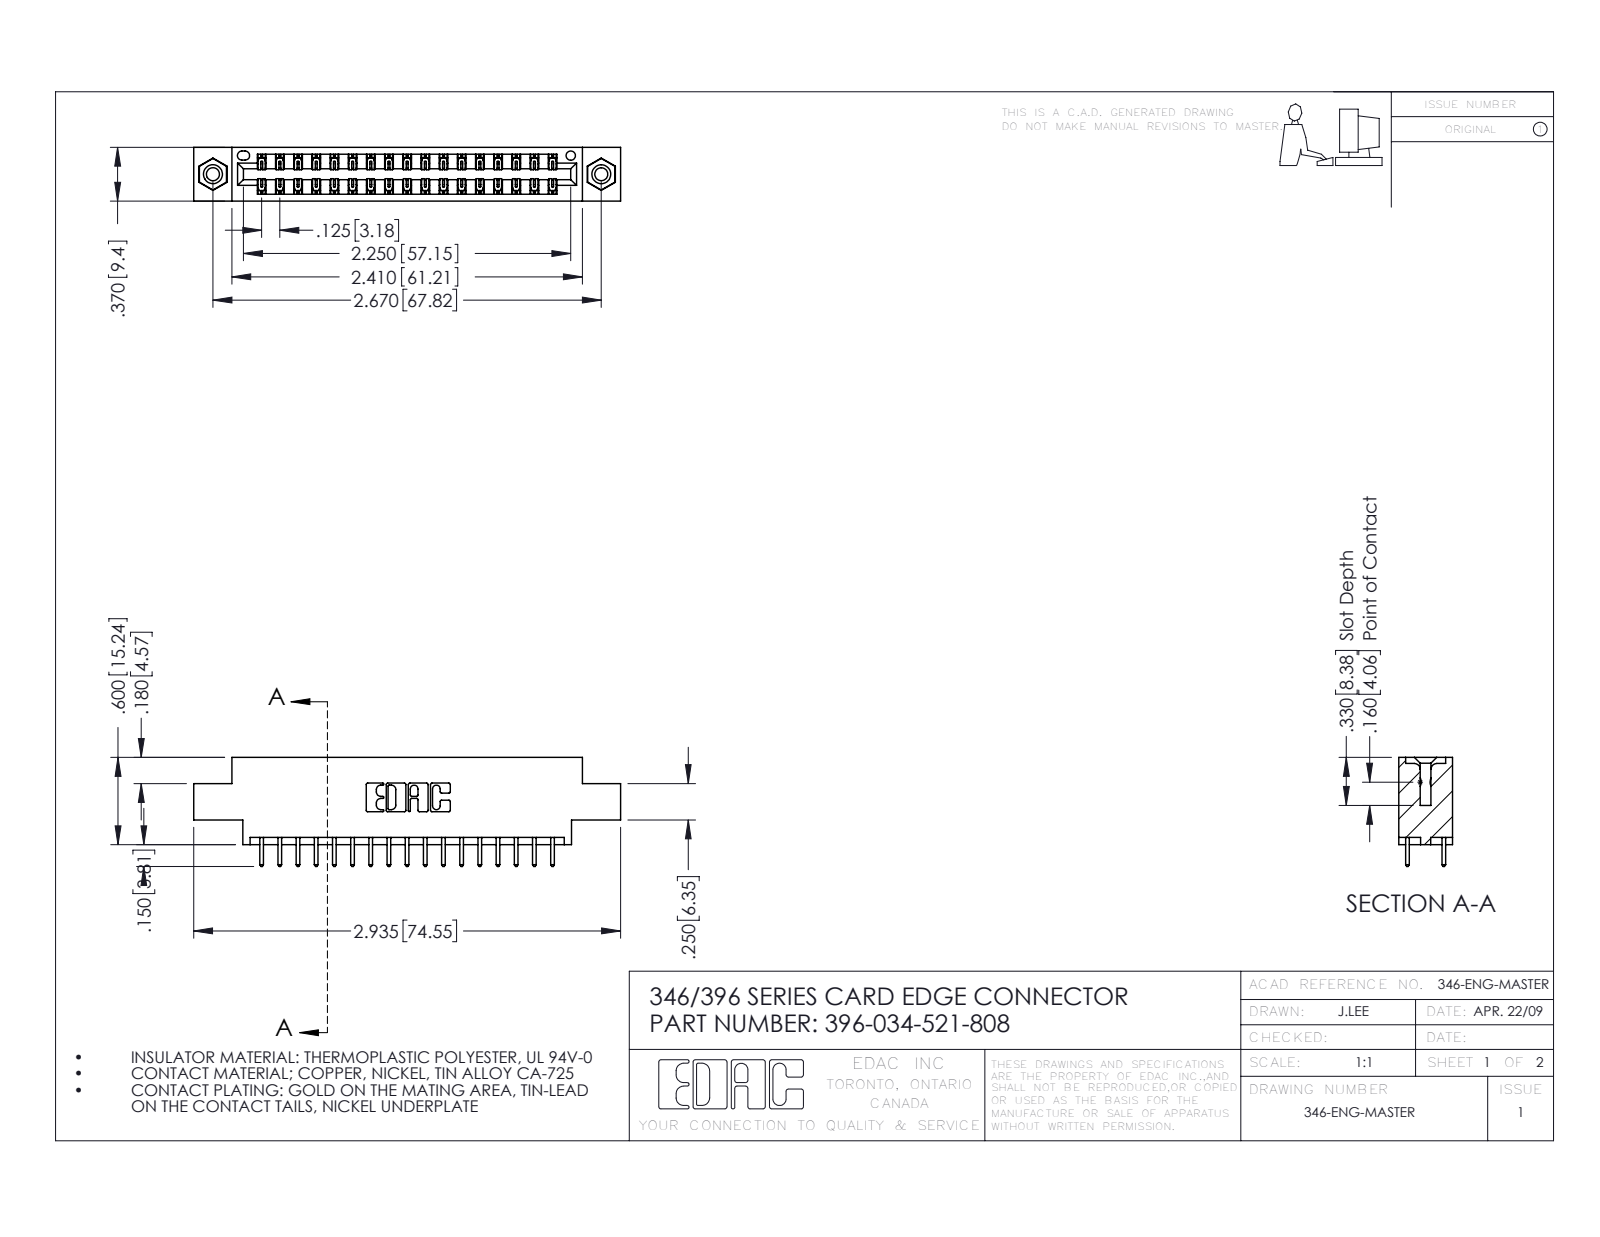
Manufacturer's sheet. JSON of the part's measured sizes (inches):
{"part_name": "345-292-001_345-293-121; 345-250-001_345-250-003-102; 396-034-521-808; 346 Part_0.170 Offset - 0.156 Dia-TI", "step_written_by": "SolidWorks 2016 (CONFIG_CONTROL_DESIGN)", "units": "inches", "bodies": {"solids": 37, "faces": 1954, "planar": 1302, "cylindrical": 636, "other": 16}, "overall_size": [2.935, 0.75, 0.37], "volume_in3": 0.421, "surface_area_in2": 14.26, "round_holes": [[0.089, 2], [0.125, 2], [0.156, 2], [0.064, 1]], "round_bosses_or_shafts": [[0.155, 2]], "partial_cylinders_radius": [[0.006, 51], [0.01, 34], [0.01, 22], [0.007, 6], [0.031, 6], [0.026, 3], [0.014, 2], [0.022, 2]], "face_to_face_distances": [0.048, 0.322, 0.25, 0.37, 0.072, 0.298, 0.025, 0.275, 0.222, 0.148], "hole_center_spacings": [0.246, 2.463, 2.67]}
